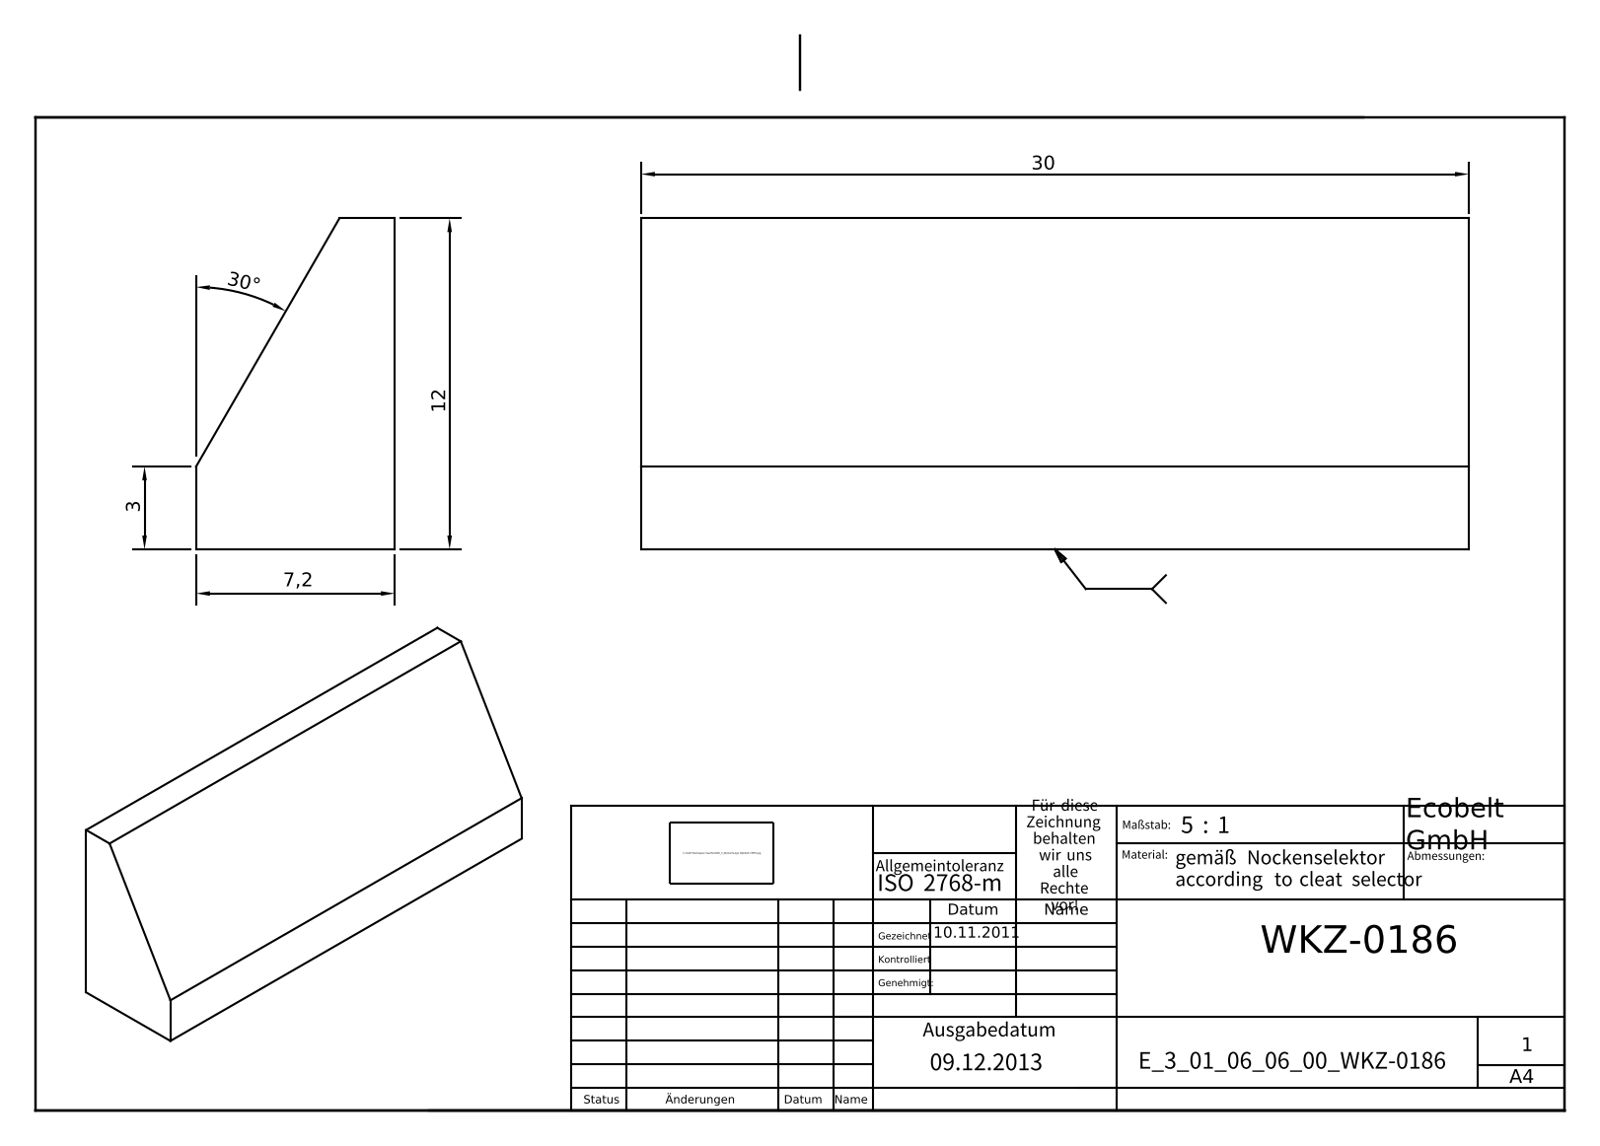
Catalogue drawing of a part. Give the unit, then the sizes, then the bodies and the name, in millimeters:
Units: millimetres
Overall size (bounding box): 30 × 12 × 7.2
Main face-to-face distances: 7.2, 30, 12
Volume: 1 891 mm³ · Surface area: 1 164 mm²
Bodies: 1 solid, 7 faces (7 planar, 0 cylindrical, 0 other)
Part name (STEP PRODUCT): E_3_01_06_06_00_WKZ-0186
STEP written by: Autodesk Inventor 2025 (AUTOMOTIVE_DESIGN)
